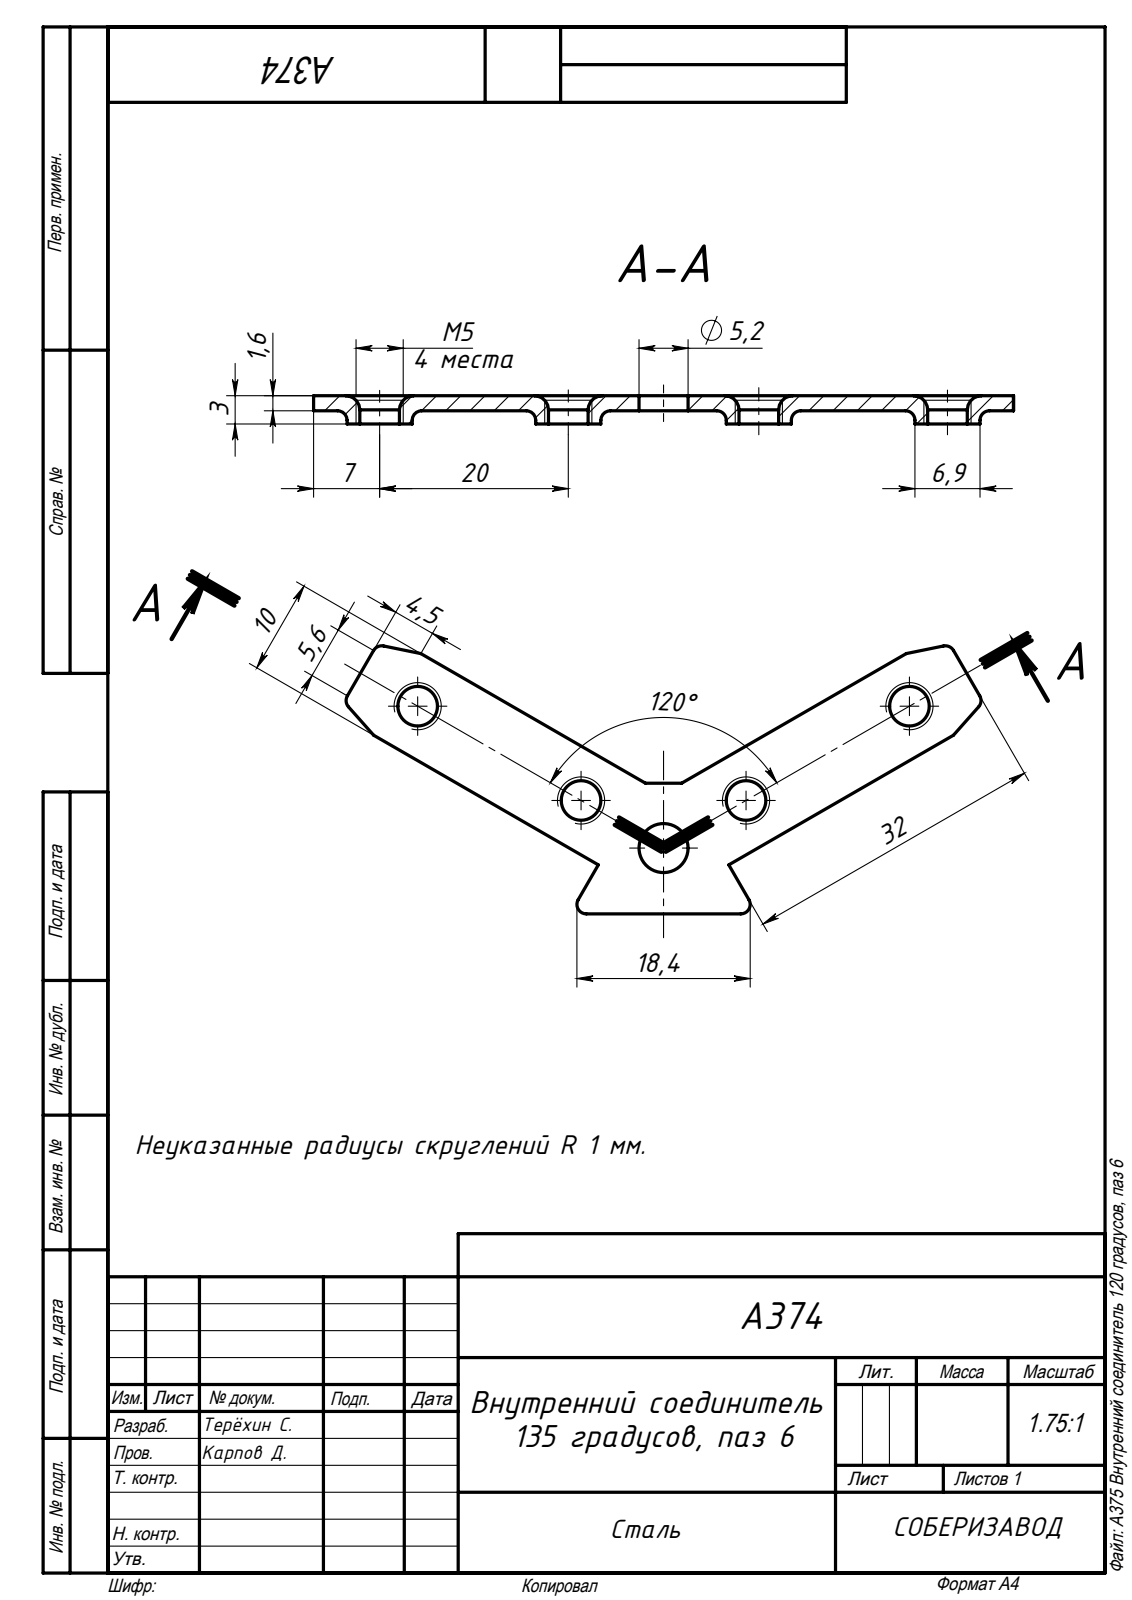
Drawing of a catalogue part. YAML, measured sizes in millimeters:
part_name: "A375 Внутренний соединитель 120 градусов, паз 6"
step_written_by: "SolidWorks 2020 (AUTOMOTIVE_DESIGN)"
units: millimeters
bodies: {solids: 1, faces: 62, planar: 20, cylindrical: 26, other: 16}
overall_size: [67.3, 28.44, 3]
volume: 1261
surface_area: 1945
round_holes:
  - {diameter: 4.2, count: 4}
  - {diameter: 5.2, count: 1}
round_bosses_or_shafts:
  - {diameter: 6.9, count: 4}
partial_cylinders:
  - {radius: 1, count: 6}
face_to_face_distances: [1.6, 1.4, 3, 10, 32, 13.86]
hole_center_spacings: [10.1, 20, 30.1, 36.23, 17.5, 52.14]
